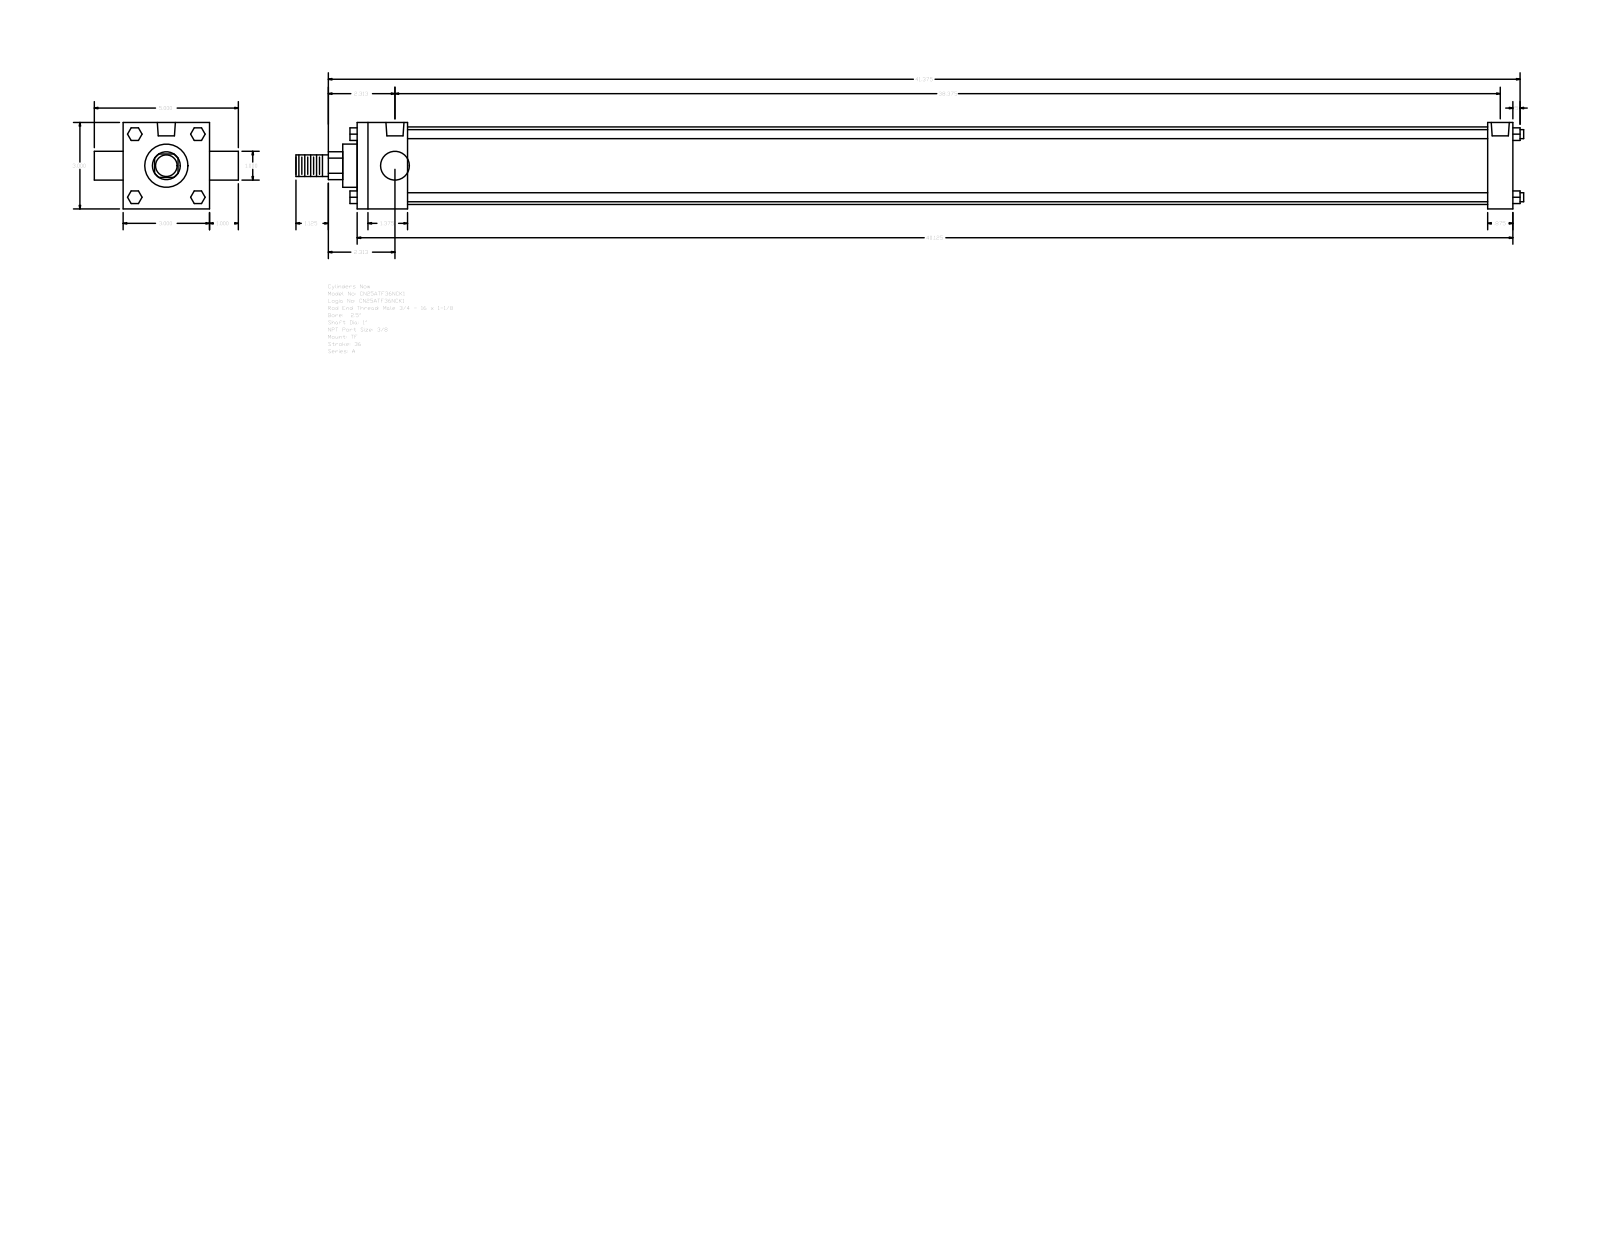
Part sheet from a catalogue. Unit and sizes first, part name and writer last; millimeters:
Units: millimetres
Overall size (bounding box): 1082.67 × 127 × 76.2
Round holes (diameter × count): ⌀5.56 ×3, ⌀15.93 ×2
Round bosses / shafts (diameter × count): ⌀7.94 ×4, ⌀25.4 ×2, ⌀68.33 ×1, ⌀38.1 ×1, ⌀19.05 ×1
Partial cylindrical surfaces — rounded edges, fillets, slot ends (radius × count): R12.29 ×1
Main face-to-face distances: 76.2, 1019.18, 44.45, 996.95, 952.5, 974.73, 22.23, 25.4, 101.6, 12.7
Hole centre spacings: 2.38, 977.1, 974.72, 979.48
Bodies: 0 solids, 120 faces (92 planar, 28 cylindrical, 0 other)
Part name (STEP PRODUCT): A_TF__0250_1
STEP written by: GSSL Pune (CONFIG_CONTROL_DESIGN)
